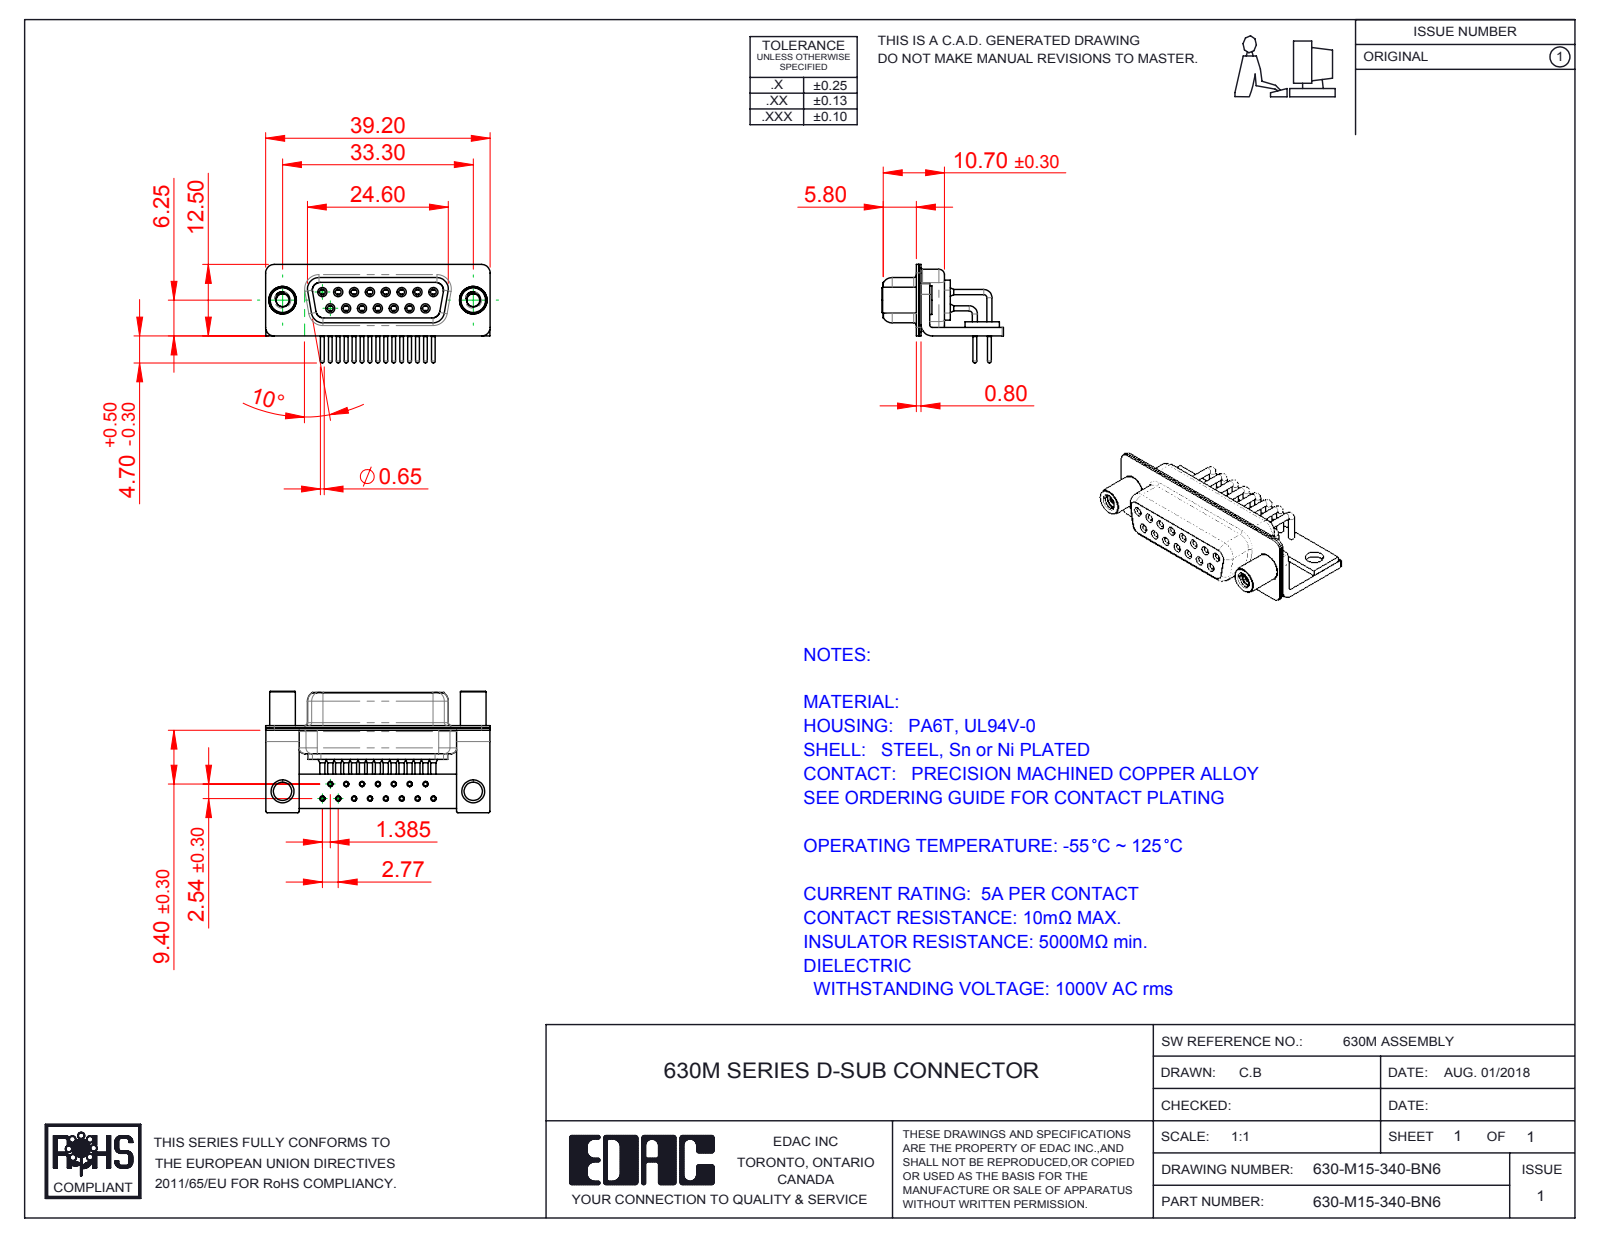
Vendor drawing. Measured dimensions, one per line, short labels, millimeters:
name: 630M Shell Front_15 Contacts; 630M Contact Row 2; 630M Stabilizer Board_15 Contacts; 630M Housing_15 Contacts (+5 more)
written by: SolidWorks 2016 (CONFIG_CONTROL_DESIGN)
unit: mm
bodies: 23 solids, 1204 faces (320 planar, 576 cylindrical, 308 other)
size: 39.2 × 21.2 × 17.2
volume: 3 171 mm³; area: 8 035 mm²
holes: 15× ⌀0.9, 15× ⌀1, 15× ⌀1.1, 15× ⌀1.7, 15× ⌀1.8, 15× ⌀2, 2× ⌀2.26, 2× ⌀3.2, 2× ⌀4, 2× ⌀4.8
bosses: 27× ⌀0.9, 15× ⌀1.6, 15× ⌀1.5, 15× ⌀0.65, 2× ⌀5, 2× ⌀4.9, 2× ⌀4.5
rounds: 16× R0.25, 16× R1.5, 13× R2, 8× R1.35, 8× R1.6, 5× R0.5, 4× R0.6, 4× R0.65
face distances: 0.4, 2.3, 1.9, 0.8, 1.5, 9.35, 1, 1.45, 8.95, 0.85
hole spacings: 2.77, 5.54, 8.31, 3.16, 4.87, 11.08, 2.89, 7.37
